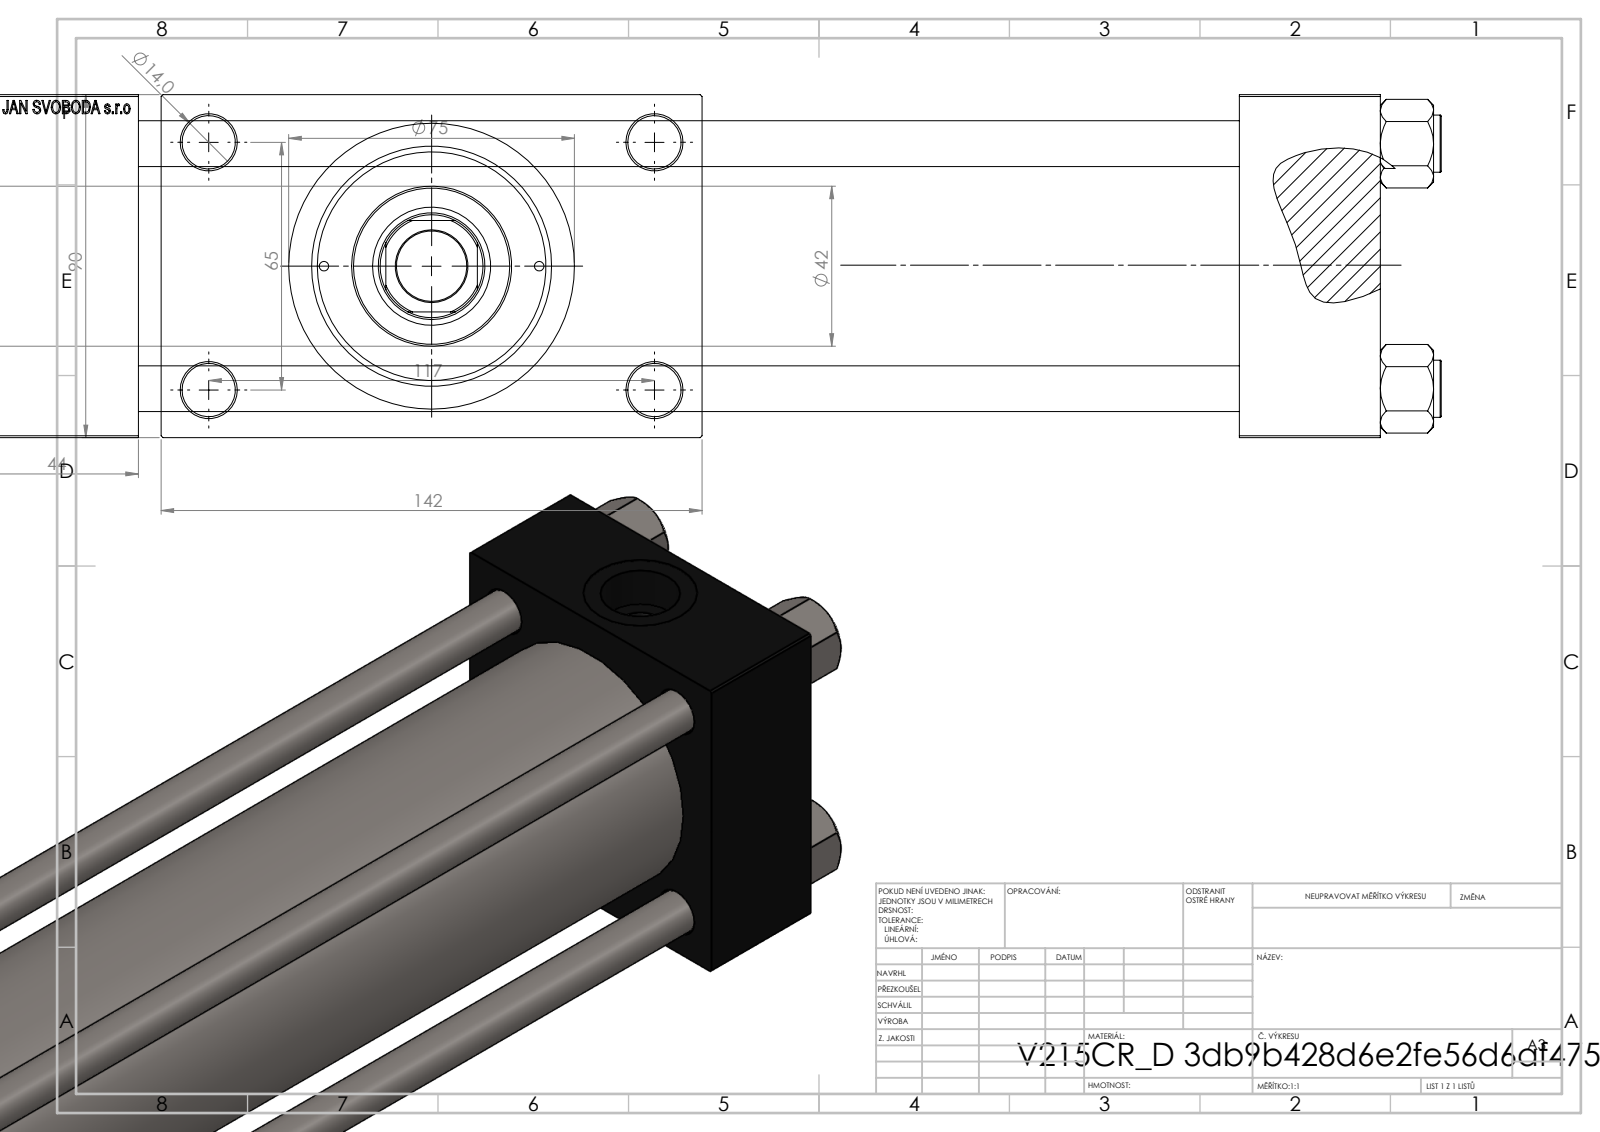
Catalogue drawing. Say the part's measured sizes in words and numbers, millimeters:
The part is named "V215_VC_A; V215CR_D_Body; V215CR_VCP_D; NUT_M5_D (+1 more)". Its 3-D file was written by "SolidWorks 2019 (CONFIG_CONTROL_DESIGN)". It is 11 solids with 1112 faces: 499 planar, 93 cylindrical and 520 other. Overall it measures 433 by 142 by 90 millimeters. Its volume is 1 494 000 cubic millimeters and its surface area 348 817 square millimeters. Round holes: 4 of diameter 12, 4 of diameter 14, 2 of diameter 2.5, 2 of diameter 7, 2 of diameter 20.96, 2 of diameter 30, 1 of diameter 18.5, 1 of diameter 28, 1 of diameter 31, 1 of diameter 50, 1 of diameter 60, 1 of diameter 63. Round bosses or shafts: 4 of diameter 15, 1 of diameter 75, 1 of diameter 69, 1 of diameter 42. Partial cylindrical surfaces (rounded edges, fillets, slot ends): 1 of radius 13.5. The main face-to-face distances are 90, 289, 37, 326, 333, 370, 44, 26, 116, 142. The hole center spacings are 26.35, 32.39, 44.4, 45.47, 64.3, 66.92, 68.42, 69.81.
